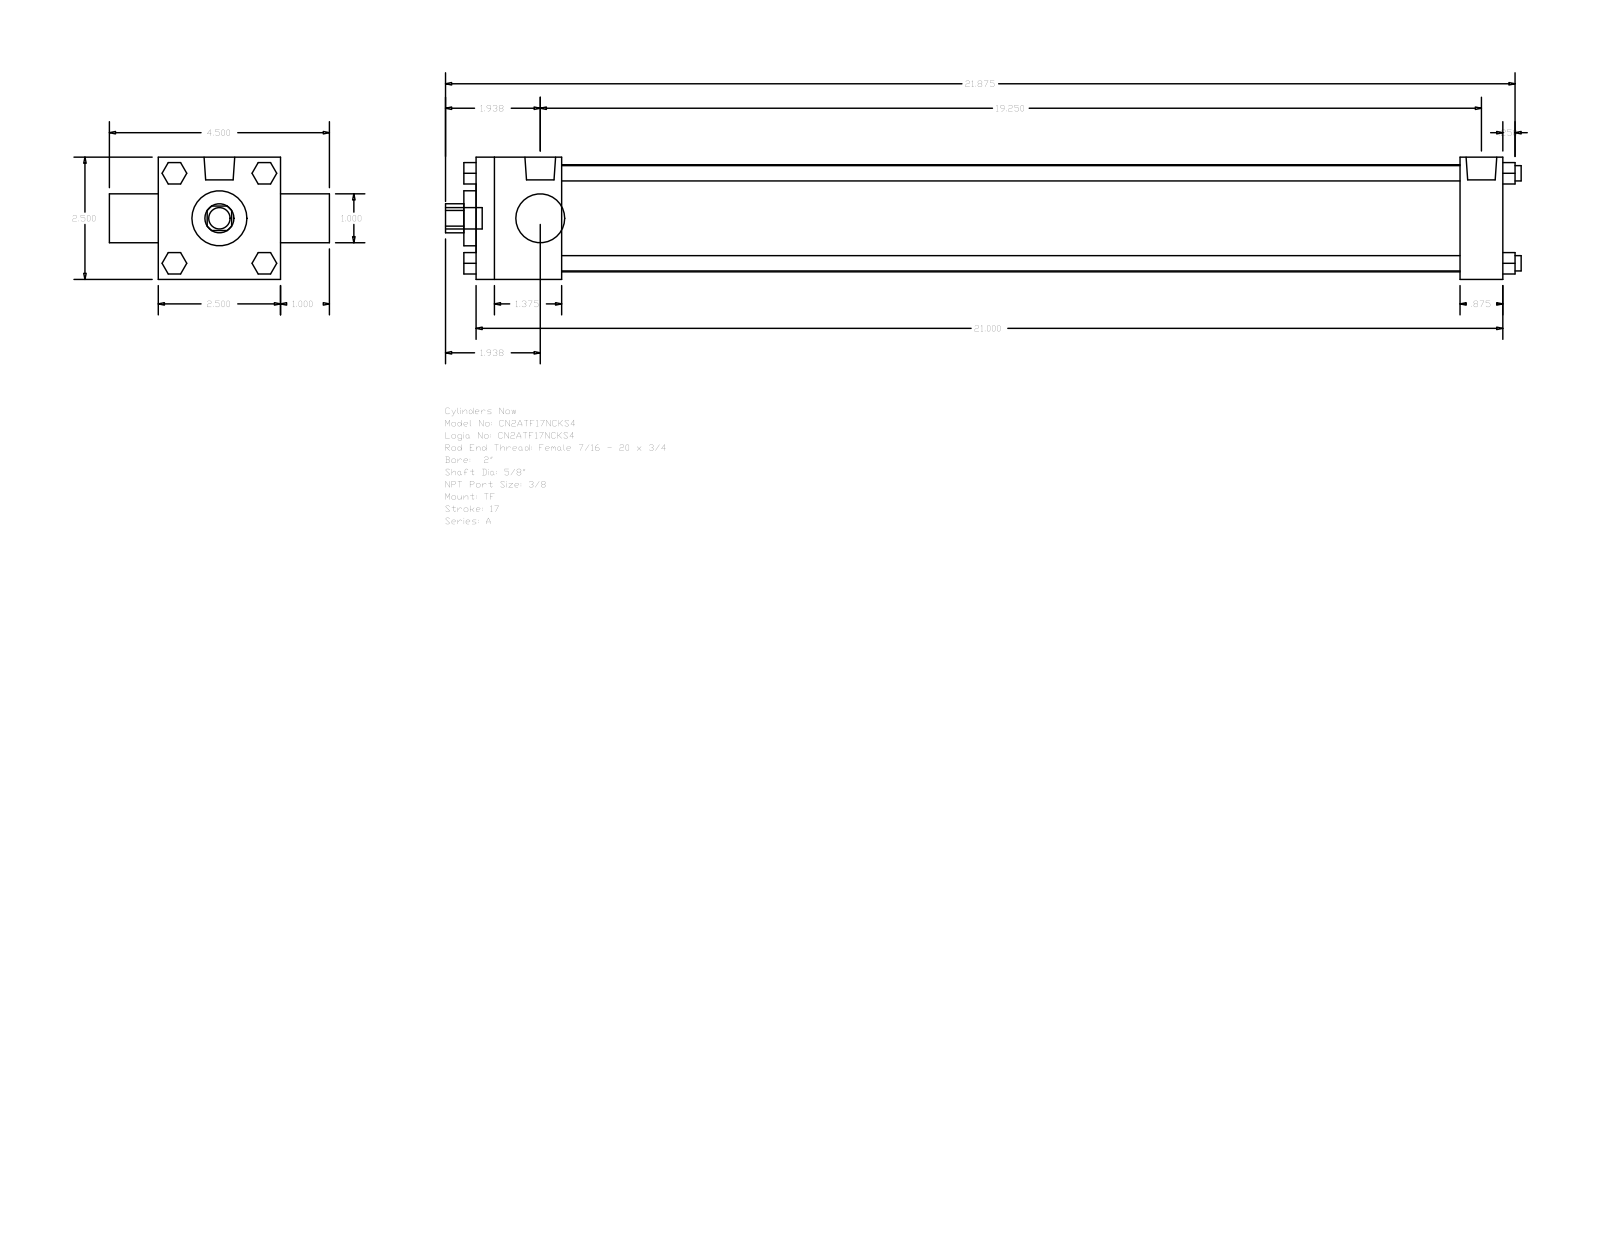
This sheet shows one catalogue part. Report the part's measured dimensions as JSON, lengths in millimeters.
{"part_name": "A_TF__0200_0.625", "step_written_by": "GSSL Pune (CONFIG_CONTROL_DESIGN)", "units": "millimeters", "bodies": {"solids": 0, "faces": 120, "planar": 92, "cylindrical": 28, "other": 0}, "overall_size": [558.8, 114.3, 63.5], "round_holes": [[15.88, 1], [25.4, 1], [28.57, 1], [55.63, 1]], "round_bosses_or_shafts": [[7.94, 4], [5.56, 3], [15.93, 2], [11.11, 1]], "partial_cylinders_radius": [[7.54, 1]], "face_to_face_distances": [63.5, 533.39, 44.45, 511.17, 466.72, 488.94, 22.22, 25.4, 88.9, 6.35]}
